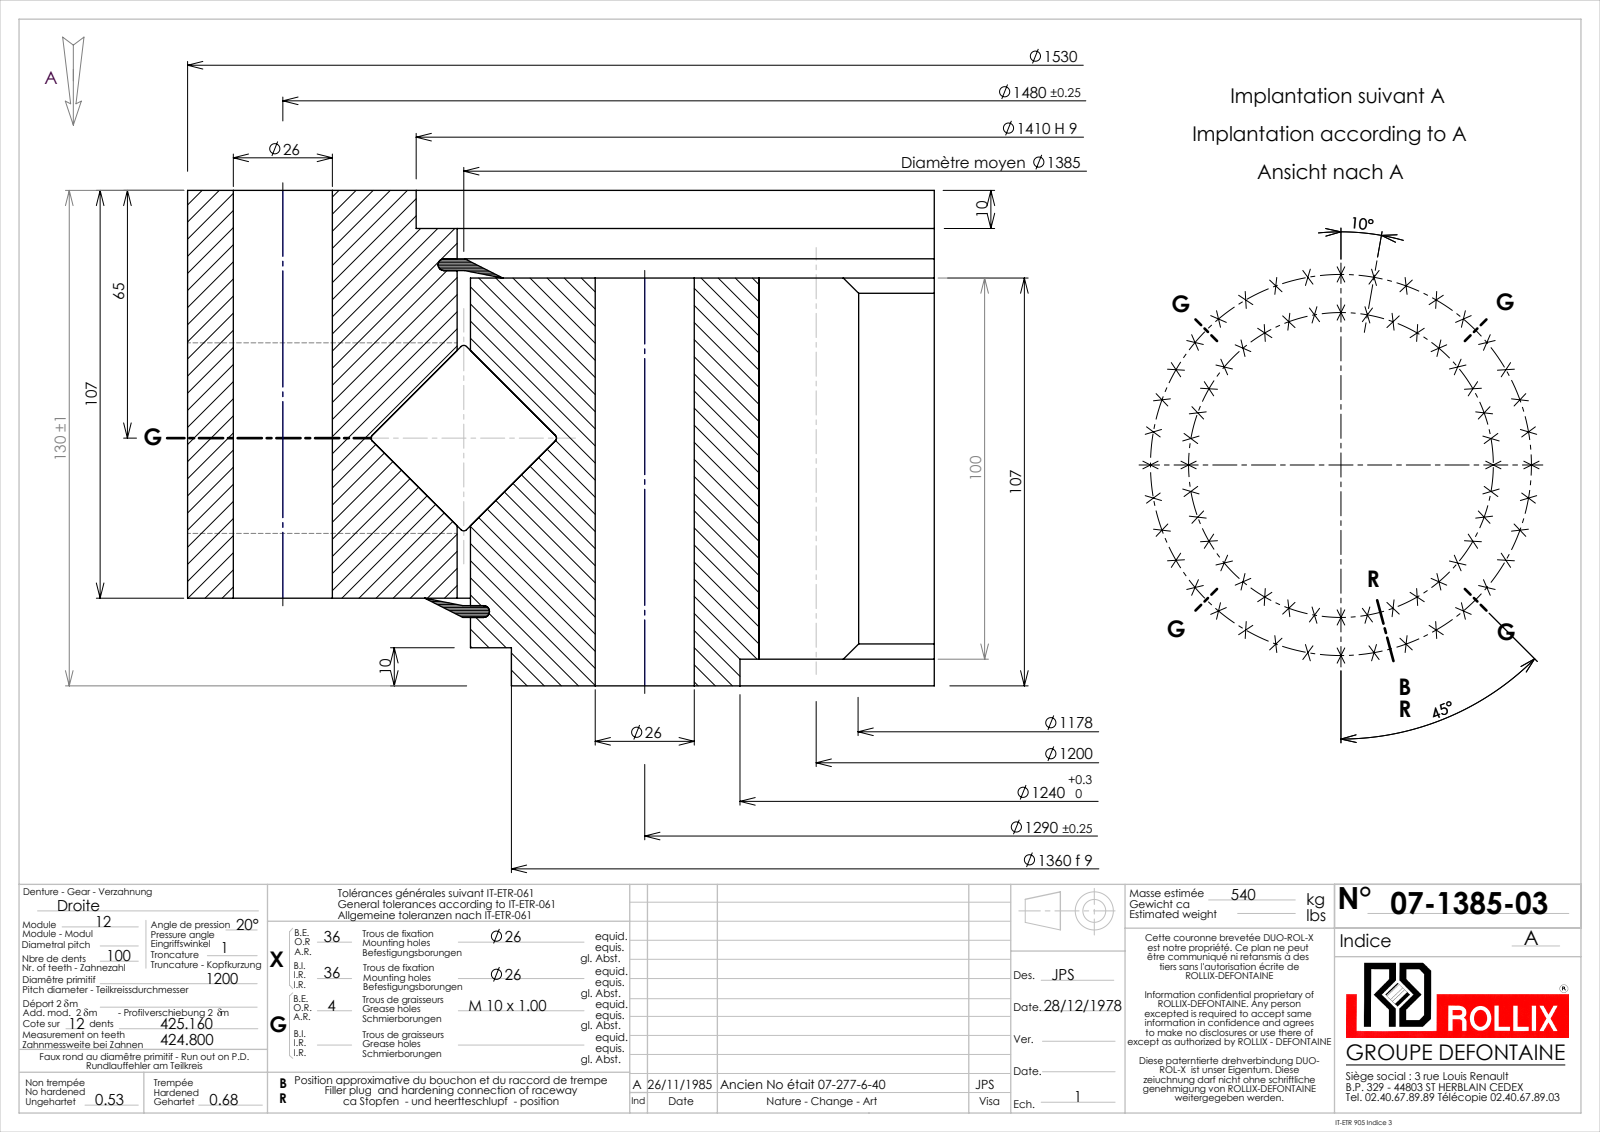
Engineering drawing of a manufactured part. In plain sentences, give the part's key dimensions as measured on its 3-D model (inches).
The part is named "07-1385-03". Its 3-D file was written by "SolidWorks 2016 (CONFIG_CONTROL_DESIGN)". It is 5 solids with 833 faces: 217 planar, 375 cylindrical and 241 other. Overall it measures 60.236 by 60.236 by 5.118 inches. Its volume is 3 887 cubic inches and its surface area 7 288 square inches. Round holes: 72 of diameter 1.024, 4 of diameter 0.354, 1 of diameter 48.819, 1 of diameter 54.665, 1 of diameter 55.512. Round bosses or shafts: 1 of diameter 60.236, 1 of diameter 54.39, 1 of diameter 53.543, 1 of diameter 1.378. Partial cylindrical surfaces (rounded edges, fillets, slot ends): 1 of radius 23.189, 1 of radius 24.213. The main face-to-face distances are 0.906, 4.213, 3.307, 5.118, 0.394, 4.724, 0.512, 3.819, 0.707, 4.411. The hole center spacings are 25.394, 4.426, 13.145, 21.464, 46.029, 8.819, 50.016, 17.37.
